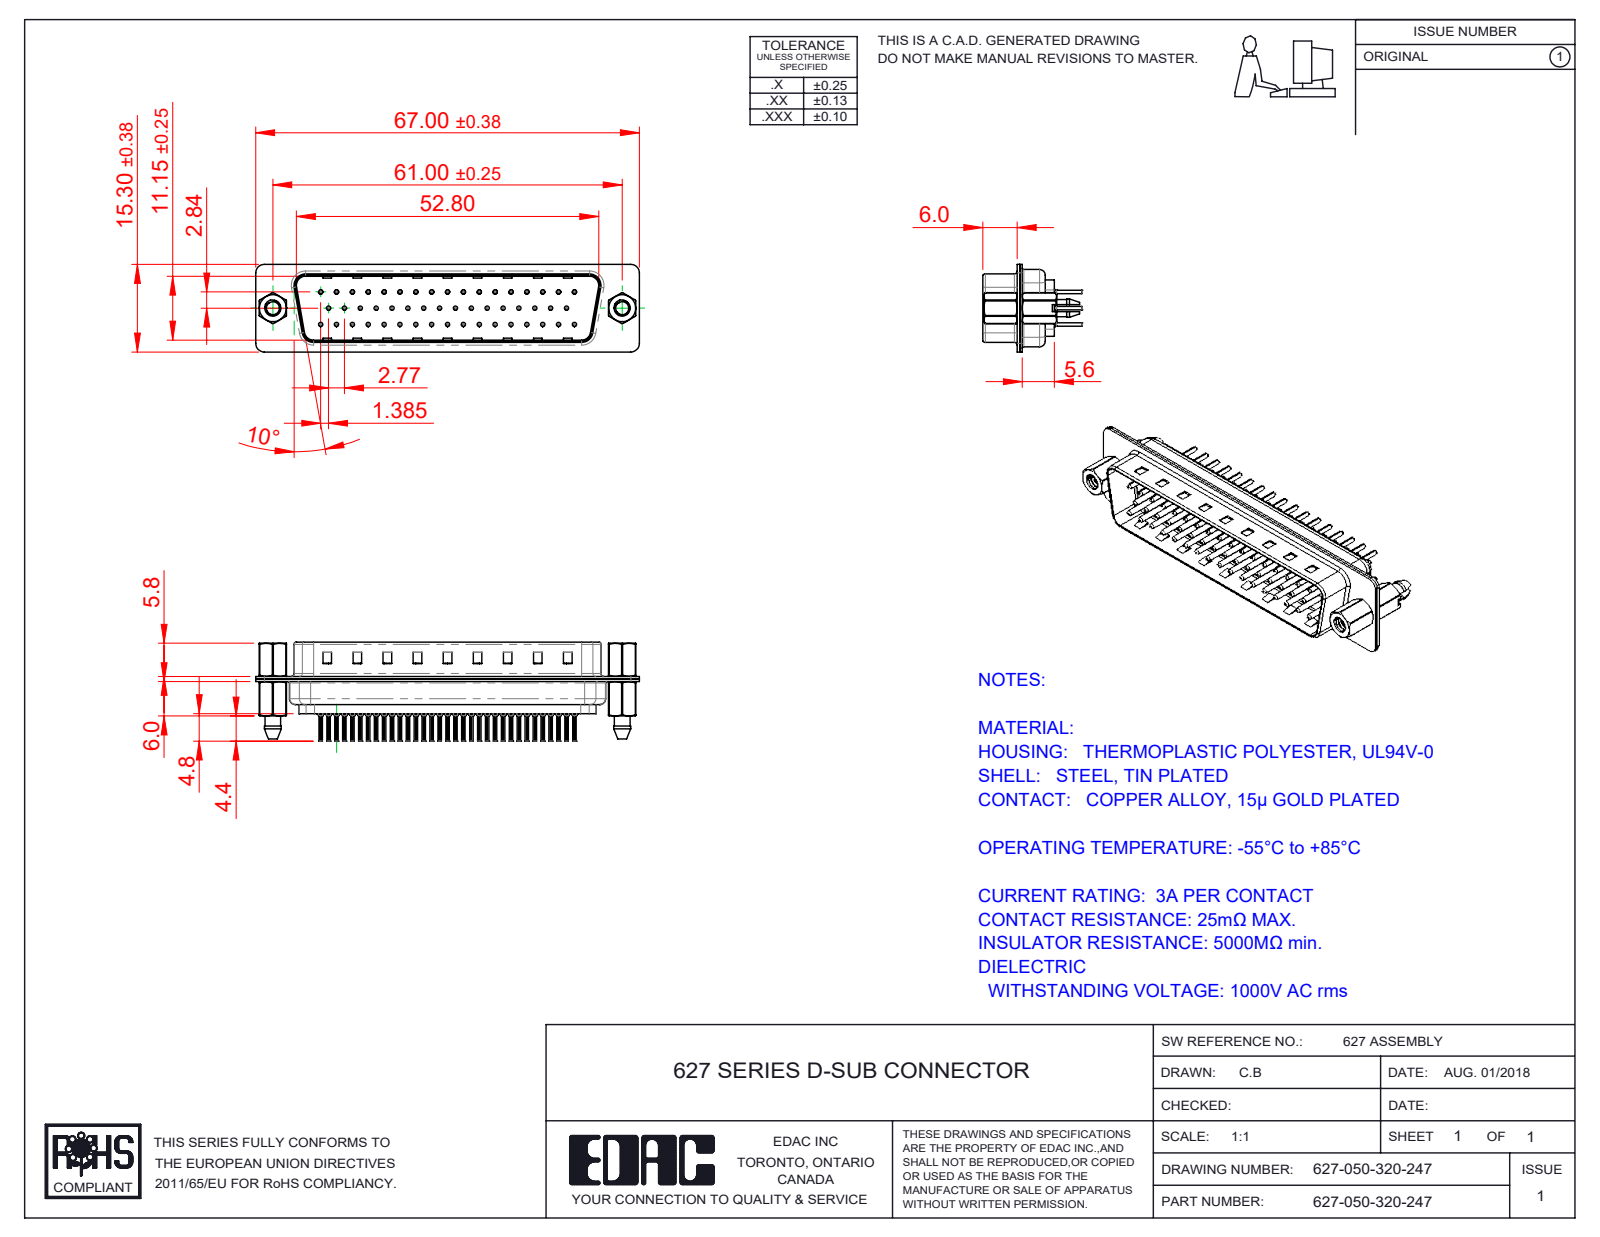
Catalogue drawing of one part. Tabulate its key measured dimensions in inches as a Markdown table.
| quantity | value |
| --- | --- |
| part name | 627-050-320-047; 627 4-40 Hex Standoff; 627 4-40 Threaded Boardlock_LP; 627 Shell Rear_50 Contacts (+5 more) |
| STEP written by | SolidWorks 2020 (CONFIG_CONTROL_DESIGN) |
| units | inches |
| bodies | 57 solids, 5512 faces (1457 planar, 2095 cylindrical, 1960 other) |
| overall size | 2.638 × 0.681 × 0.602 |
| volume | 0.29 in³ |
| surface area | 20.7 in² |
| round holes (diameter × count) | 0.008 × 50, 0.014 × 50, 0.043 × 50, 0.063 × 50, 0.089 × 2, 0.09 × 2, 0.157 × 2, 0.189 × 2 |
| round bosses / shafts (diameter × count) | 0.079 × 50, 0.059 × 50, 0.03 × 50, 0.024 × 50, 0.193 × 2, 0.11 × 2 |
| partial cylindrical surfaces (radius × count) | 0.004 × 100, 0.059 × 18, 0.079 × 12, 0.063 × 10, 0.02 × 8, 0.01 × 4, 0.024 × 4, 0.026 × 4 |
| main face-to-face distances | 0.016, 0.018, 0.455, 0.035, 0.238, 0.256, 0.031, 0.485, 0.077, 0.03 |
| hole center spacings | 0.124, 0.109, 0.218, 0.327, 0.436, 0.545, 0.654, 0.198 |
